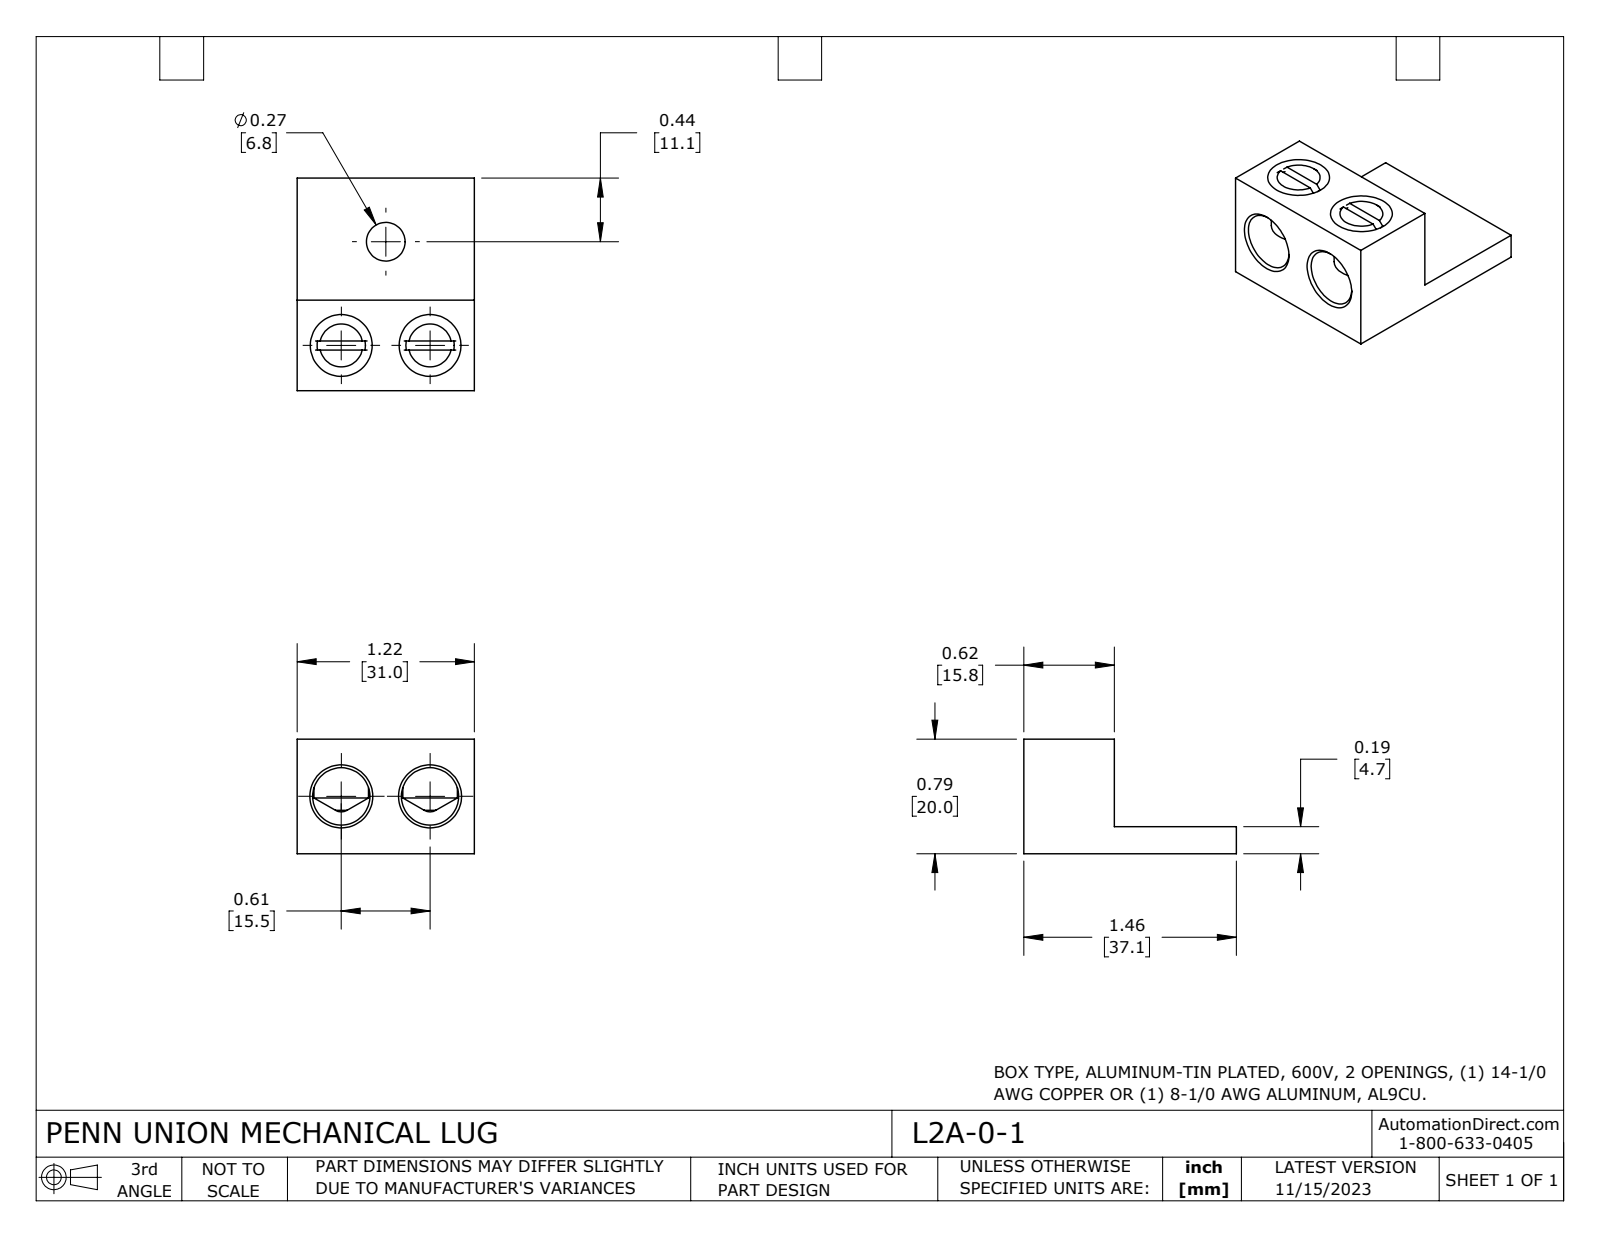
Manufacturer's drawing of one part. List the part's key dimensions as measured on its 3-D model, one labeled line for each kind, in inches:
Part name (STEP PRODUCT): L2A-0-1
STEP written by: SolidWorks 2023 (CONFIG_CONTROL_DESIGN)
Units: inches
Bodies: 3 solids, 50 faces (18 planar, 14 cylindrical, 18 other)
Overall size (bounding box): 1.461 × 1.219 × 0.787
Volume: 0.675 in³ · Surface area: 9.393 in²
Round holes (diameter × count): ⌀0.332 ×2, ⌀0.394 ×2, ⌀0.266 ×1
Round bosses / shafts (diameter × count): ⌀0.375 ×2
Main face-to-face distances: 0.185, 1.218, 0.787, 0.602, 0.622, 1.461, 0.839, 0.28, 0.342, 1.119
Hole centre spacings: 0.61, 0.775, 0.776
